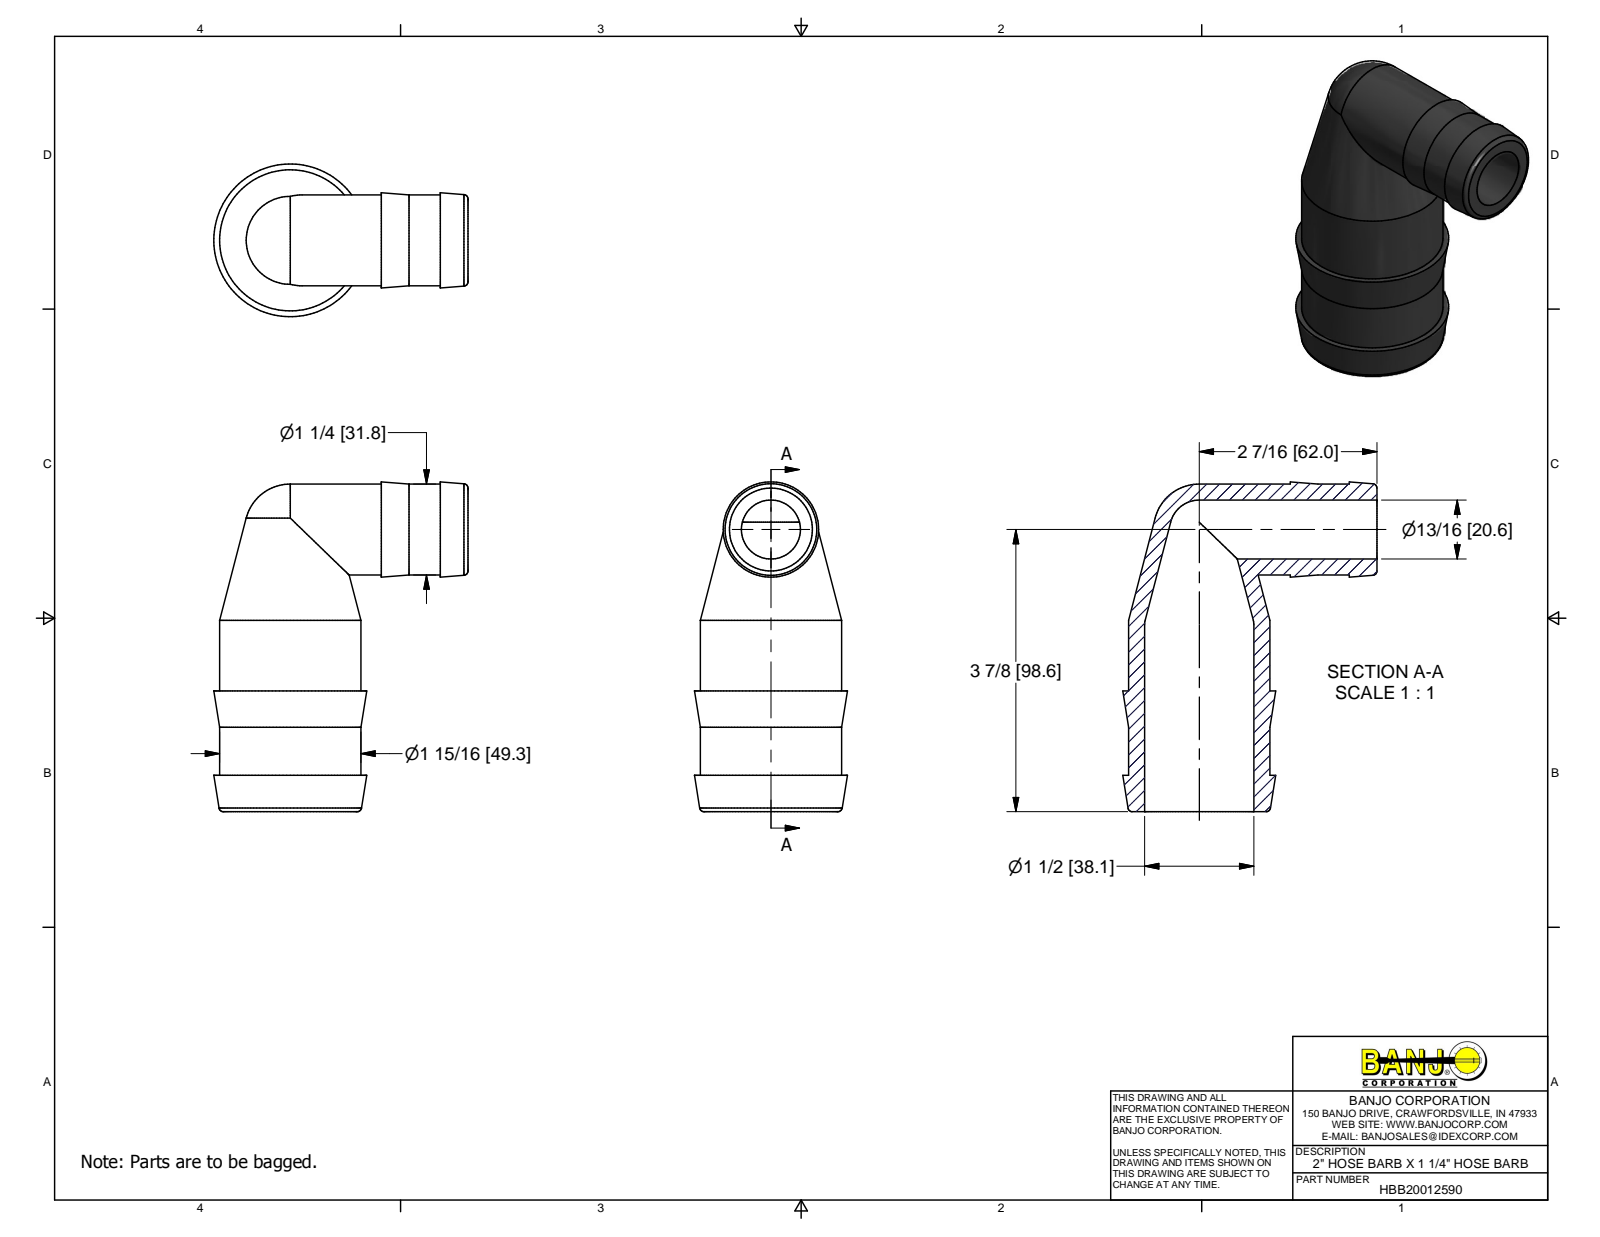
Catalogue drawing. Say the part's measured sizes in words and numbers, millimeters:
The part is named "HBB20012590". Its 3-D file was written by "Autodesk Inventor 2014 (AUTOMOTIVE_DESIGN)". It is 1 solid with 23 faces: 6 planar, 6 cylindrical and 11 other. Overall it measures 115.19 by 88.65 by 53.34 millimeters. Its volume is 103 212 cubic millimeters and its surface area 37 397 square millimeters. Round holes: 1 of diameter 20.57, 1 of diameter 38.1. Round bosses or shafts: 1 of diameter 49.28, 1 of diameter 31.75. The main face-to-face distances are 12.7, 42.16, 29.46, 20.57, 30.23, 9.66.
